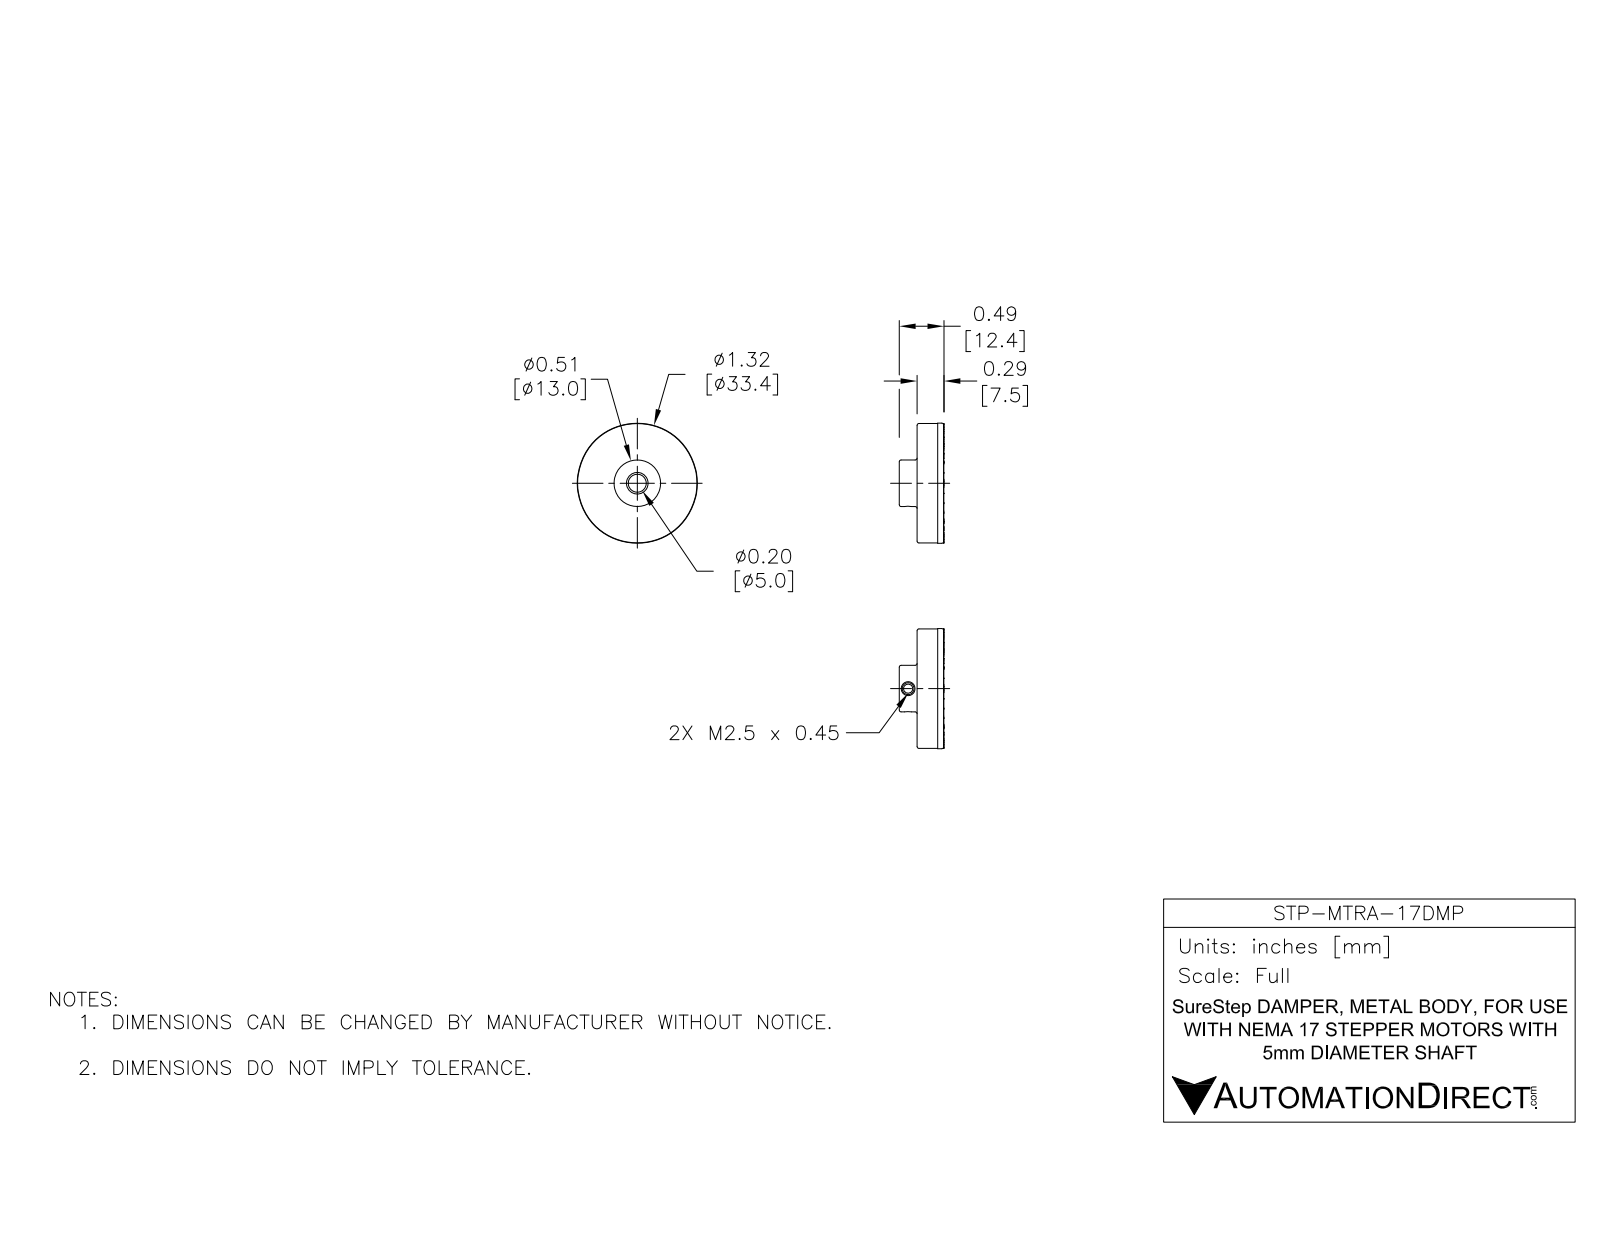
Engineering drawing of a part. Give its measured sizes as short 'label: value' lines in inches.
name: STP-MTRA-17DMP b7
written by: SolidWorks 2017 (AUTOMOTIVE_DESIGN)
unit: in
bodies: 1 solid, 309 faces (224 planar, 41 cylindrical, 44 other)
size: 1.316 × 1.316 × 0.49
volume: 0.218 in³; area: 9.622 in²
holes: 2× ⌀0.079, 1× ⌀0.197, 1× ⌀0.371, 1× ⌀0.375, 1× ⌀0.466, 1× ⌀1.106, 1× ⌀1.196, 1× ⌀1.272
bosses: 1× ⌀1.316, 1× ⌀1.31, 1× ⌀1.308, 1× ⌀1.246, 1× ⌀1.14, 1× ⌀0.51, 1× ⌀0.5, 1× ⌀0.414
face distances: 0.293, 0.041, 0.252, 0.261, 0.22, 0.032, 0.166, 0.125, 0.095, 0.127
